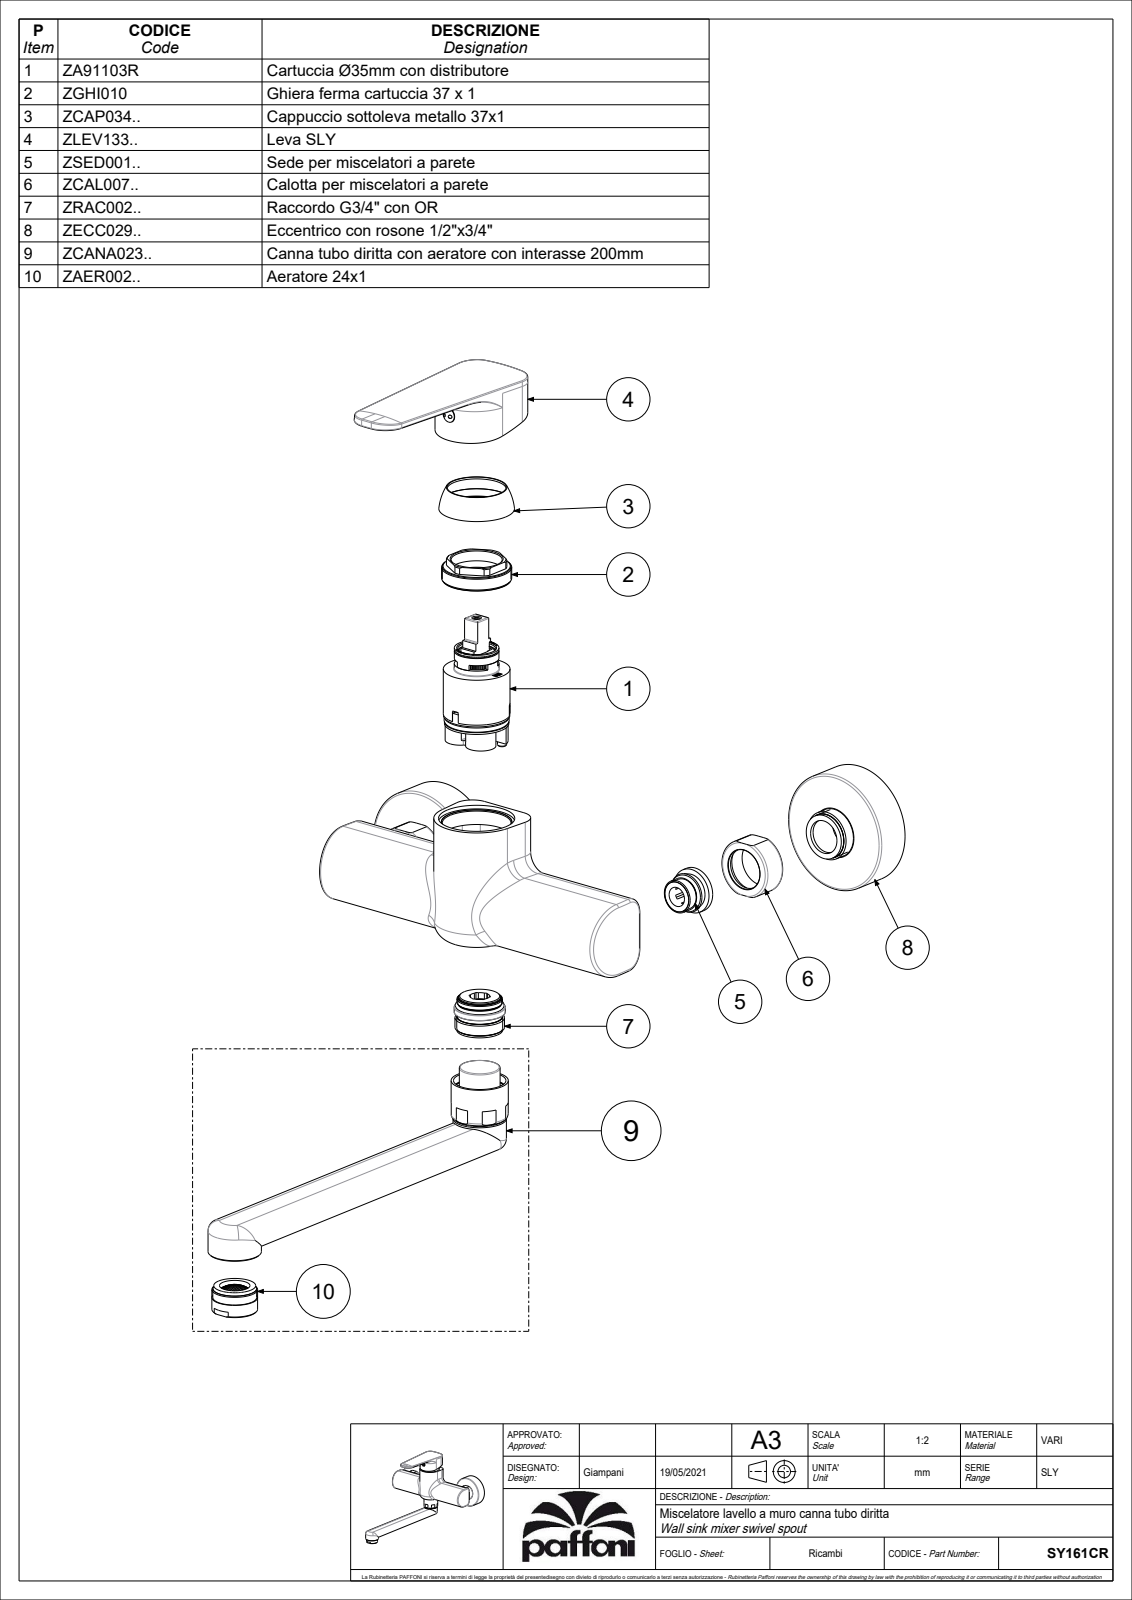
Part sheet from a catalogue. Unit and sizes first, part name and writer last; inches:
Units: inches
Overall size (bounding box): 10.591 × 8.406 × 5.787
Round holes (diameter × count): ⌀0.197 ×3, ⌀0.354 ×3, ⌀0.472 ×3, ⌀0.65 ×3, ⌀0.965 ×3, ⌀0.13 ×2, ⌀0.157 ×2, ⌀0.315 ×2, ⌀0.413 ×2, ⌀0.709 ×2, ⌀0.768 ×2, ⌀0.85 ×2
Round bosses / shafts (diameter × count): ⌀0.945 ×3, ⌀2.5 ×2, ⌀1.102 ×2, ⌀1.063 ×2, ⌀0.925 ×2, ⌀0.315 ×2, ⌀0.189 ×2, ⌀1.378 ×1
Partial cylindrical surfaces — rounded edges, fillets, slot ends (radius × count): R0.02 ×44, R0.006 ×11, R0.012 ×9, R0.059 ×6, R0.276 ×6, R0.394 ×6, R0.039 ×4, R0.256 ×4
Main face-to-face distances: 0.591, 0.138, 0.039, 0.024, 0.728, 0.63, 0.614, 1.516, 0.752, 1.437
Hole centre spacings: 0.028, 0.335, 0.339, 0.388, 0.404, 0.406, 0.461, 0.513
Volume: 13.33 in³ · Surface area: 282.2 in²
Bodies: 4 solids, 3016 faces (2214 planar, 460 cylindrical, 342 other)
Part name (STEP PRODUCT): SY161CR
STEP written by: CREO PARAMETRIC BY PTC INC, 2020044 (CONFIG_CONTROL_DESIGN)
